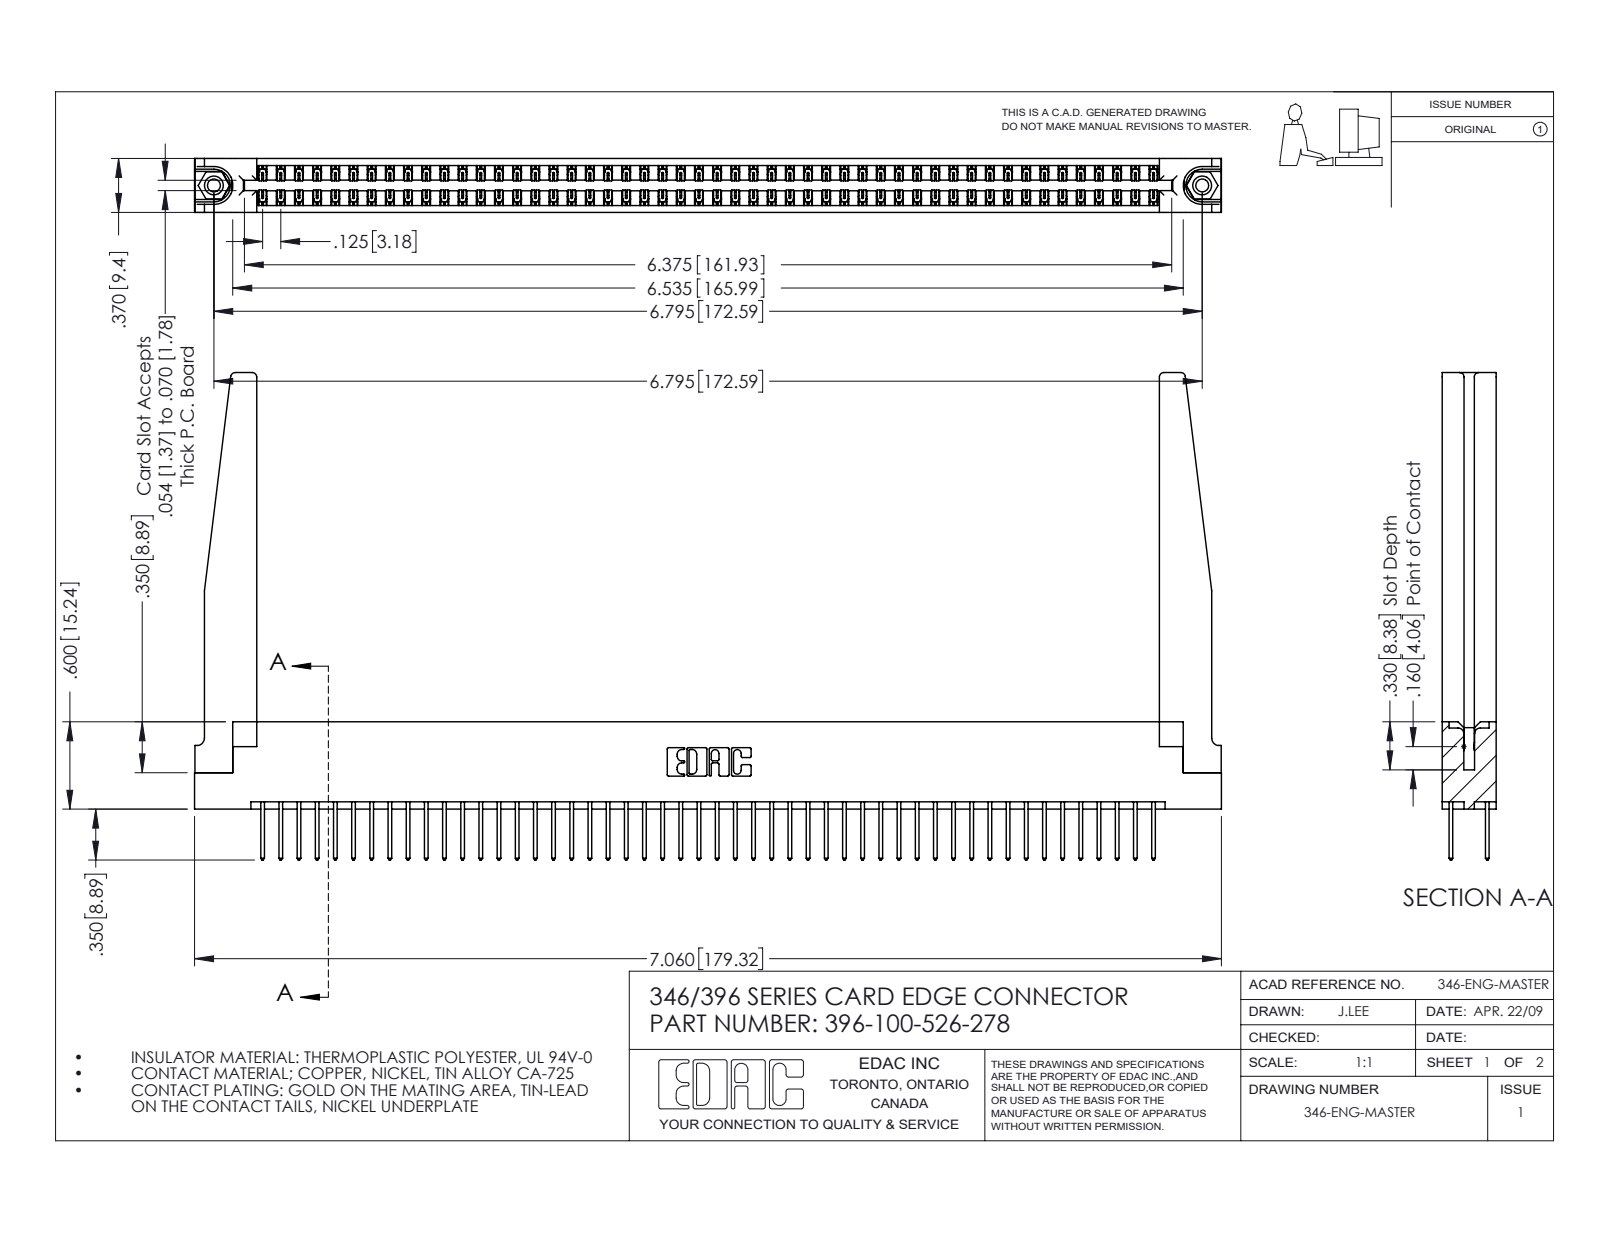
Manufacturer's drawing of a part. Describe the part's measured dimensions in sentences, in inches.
The part is named "396-100-526-278; 346 Part_Flush Mounting Lugs - 0.156 Dia-TH; 346-220-078_345-220-078; 345-250-001_345-250-001-102 (+1 more)". Its 3-D file was written by "SolidWorks 2016 (CONFIG_CONTROL_DESIGN)". It is 105 solids with 5556 faces: 3718 planar, 1786 cylindrical and 52 other. Overall it measures 7.06 by 3.35 by 0.37 inches. Its volume is 1.502 cubic inches and its surface area 49.2 square inches. Round holes: 2 of diameter 0.089, 2 of diameter 0.125, 2 of diameter 0.156, 1 of diameter 0.064. Round bosses or shafts: 2 of diameter 0.155. Partial cylindrical surfaces (rounded edges, fillets, slot ends): 150 of radius 0.006, 100 of radius 0.01, 22 of radius 0.01, 8 of radius 0.03, 6 of radius 0.007, 6 of radius 0.031, 3 of radius 0.026, 2 of radius 0.014. The main face-to-face distances are 0.048, 0.322, 0.37, 0.072, 0.25, 0.298, 0.025, 0.148, 0.15, 0.275. The hole center spacings are 0.246, 6.586, 6.795.
